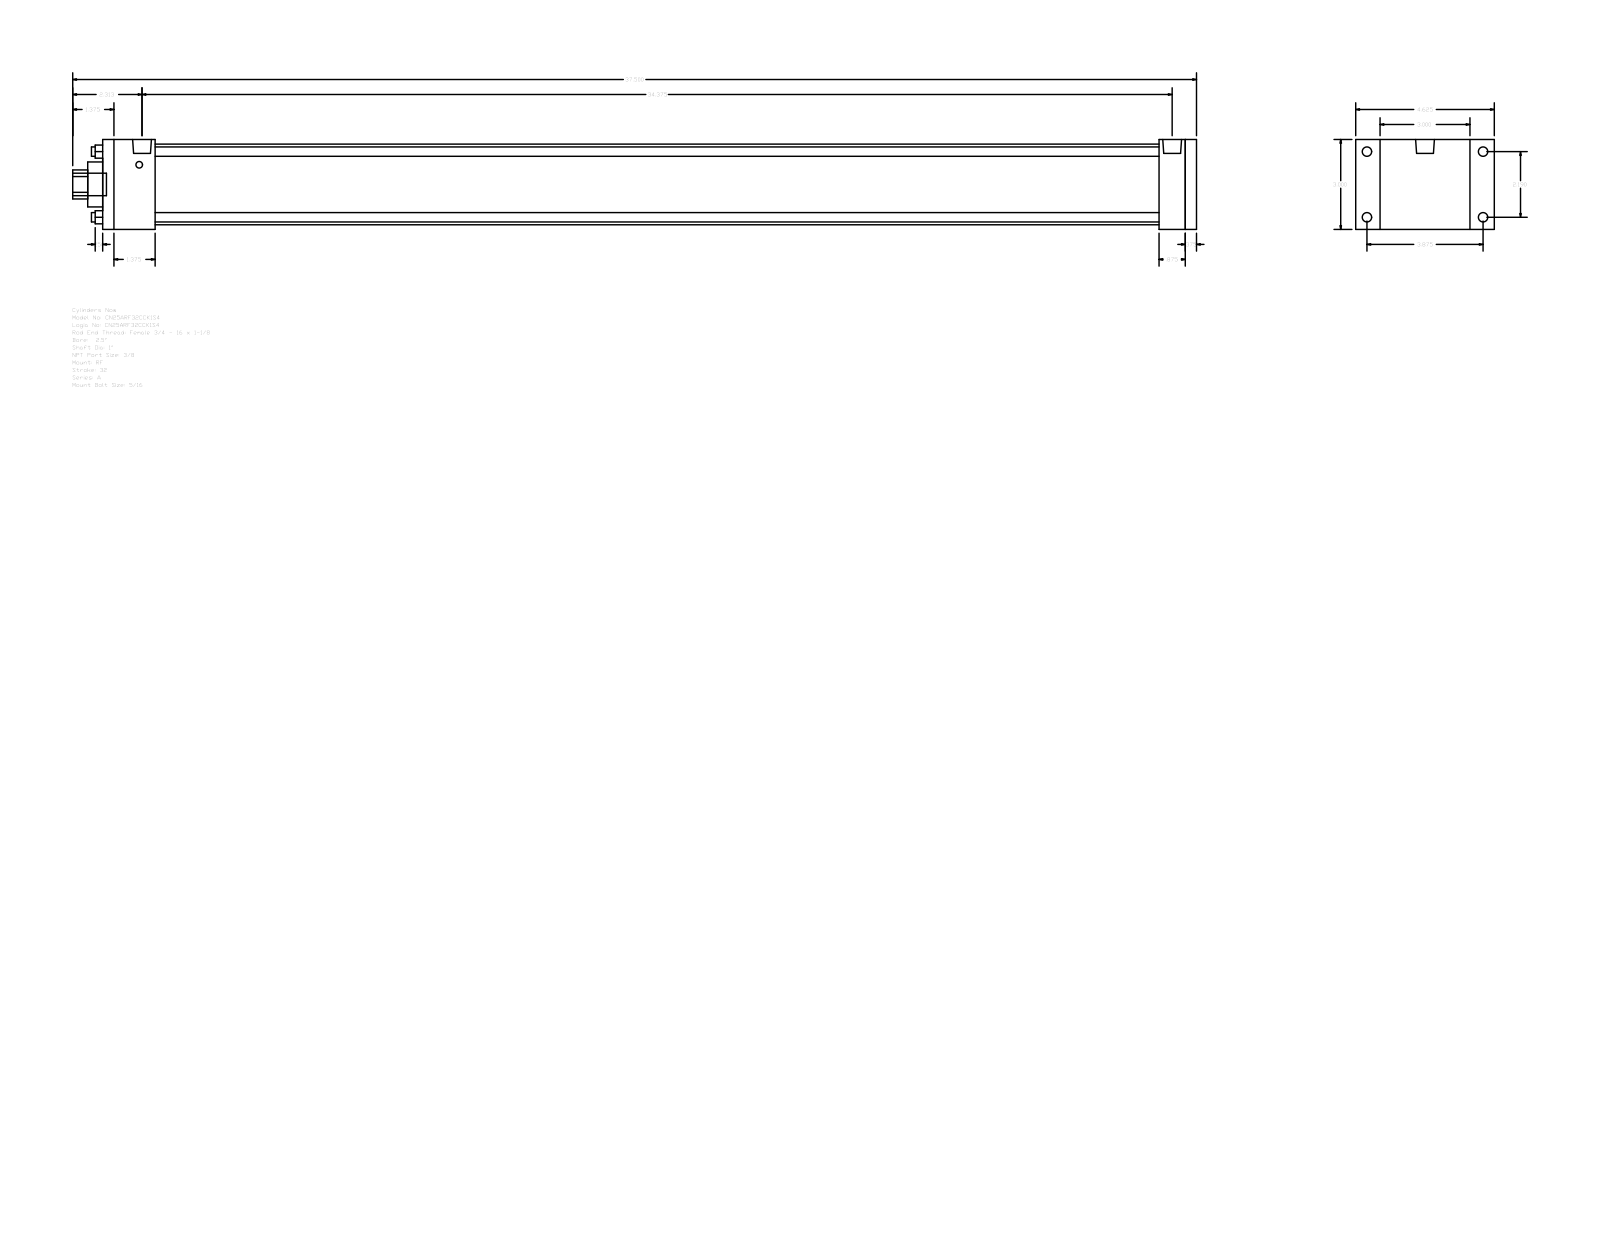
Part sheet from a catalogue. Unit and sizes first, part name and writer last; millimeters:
Units: millimetres
Overall size (bounding box): 952.5 × 117.47 × 76.2
Round holes (diameter × count): ⌀7.94 ×4, ⌀25.4 ×1, ⌀38.1 ×1, ⌀68.33 ×1
Round bosses / shafts (diameter × count): ⌀7.94 ×4, ⌀5.56 ×4, ⌀15.93 ×2, ⌀19.05 ×1
Partial cylindrical surfaces — rounded edges, fillets, slot ends (radius × count): R12.29 ×1
Main face-to-face distances: 76.2, 927.1, 9.52, 917.58, 44.45, 895.35, 850.9, 873.13, 882.65, 22.23
Hole centre spacings: 39.33, 55.62, 78.66
Bodies: 0 solids, 92 faces (64 planar, 28 cylindrical, 0 other)
Part name (STEP PRODUCT): A_RF__0250_1
STEP written by: GSSL Pune (CONFIG_CONTROL_DESIGN)
